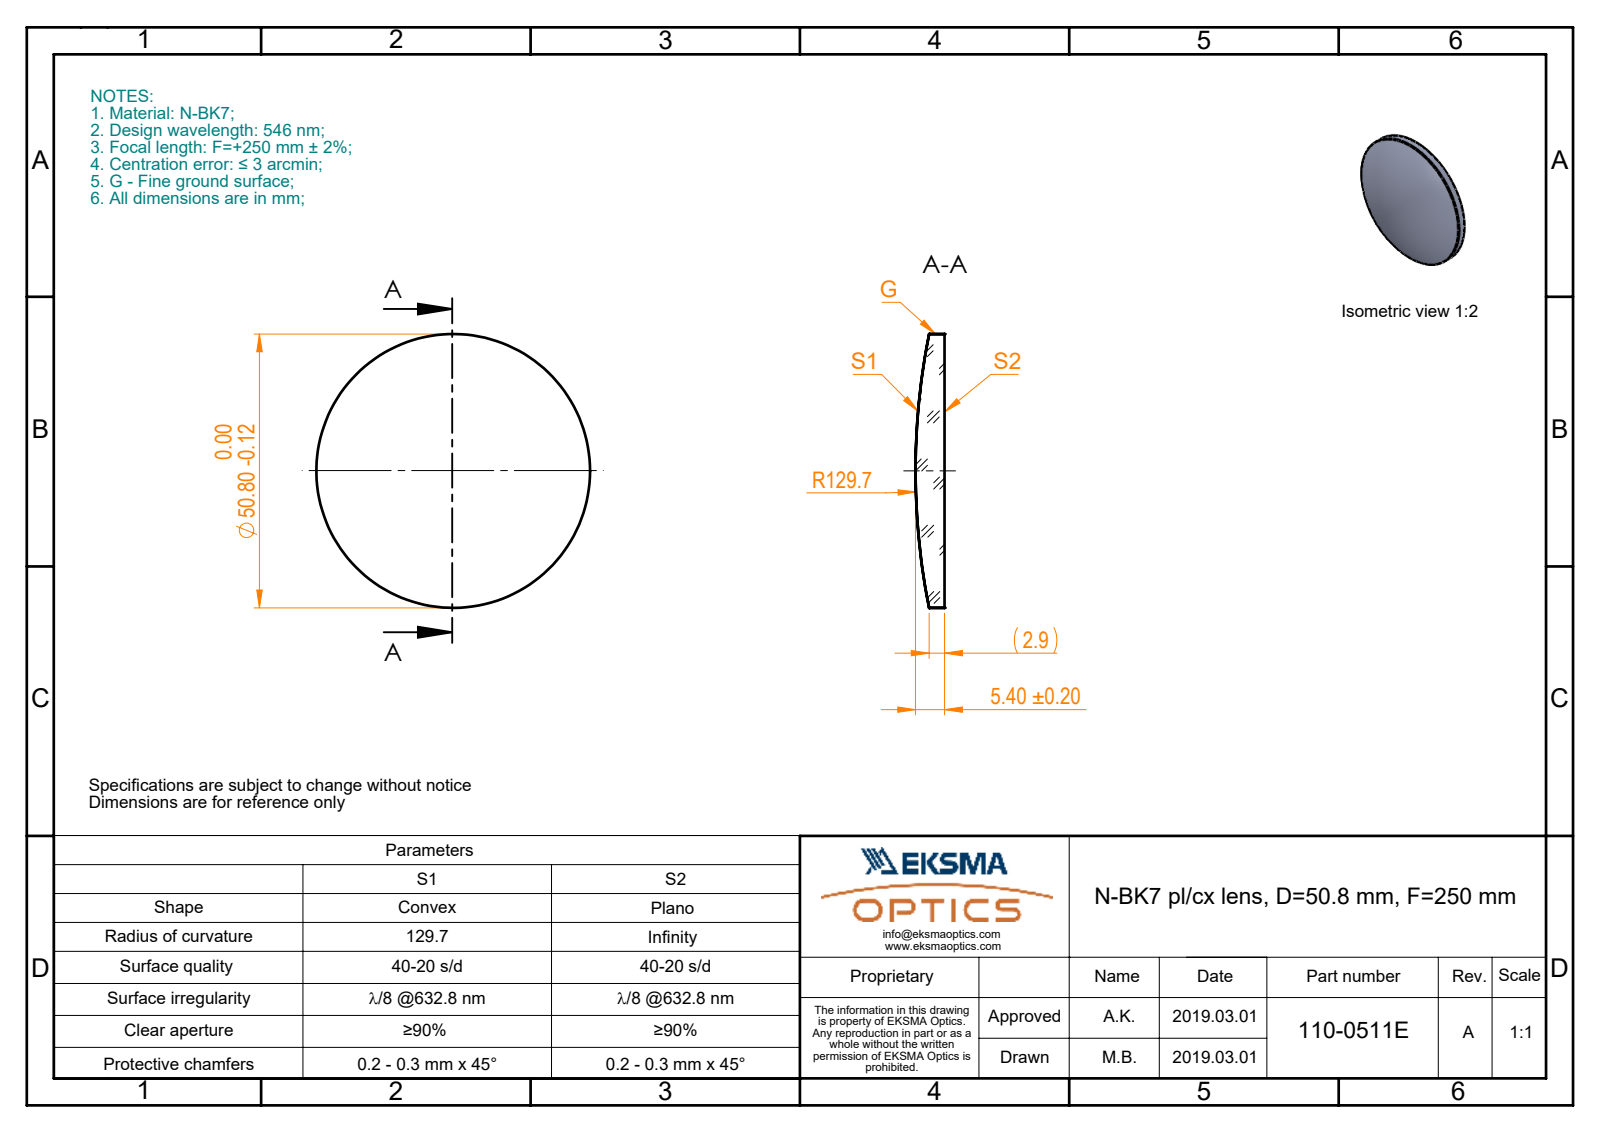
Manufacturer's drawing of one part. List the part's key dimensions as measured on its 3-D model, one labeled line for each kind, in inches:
Part name (STEP PRODUCT): 110-0511E BK7 pl-cx 50.8 F250
STEP written by: SolidWorks 2017 (CONFIG_CONTROL_DESIGN)
Units: inches
Bodies: 1 solid, 5 faces (1 planar, 2 cylindrical, 2 other)
Overall size (bounding box): 2 × 2 × 0.213
Volume: 0.513 in³ · Surface area: 7.028 in²
Round bosses / shafts (diameter × count): ⌀2 ×1
